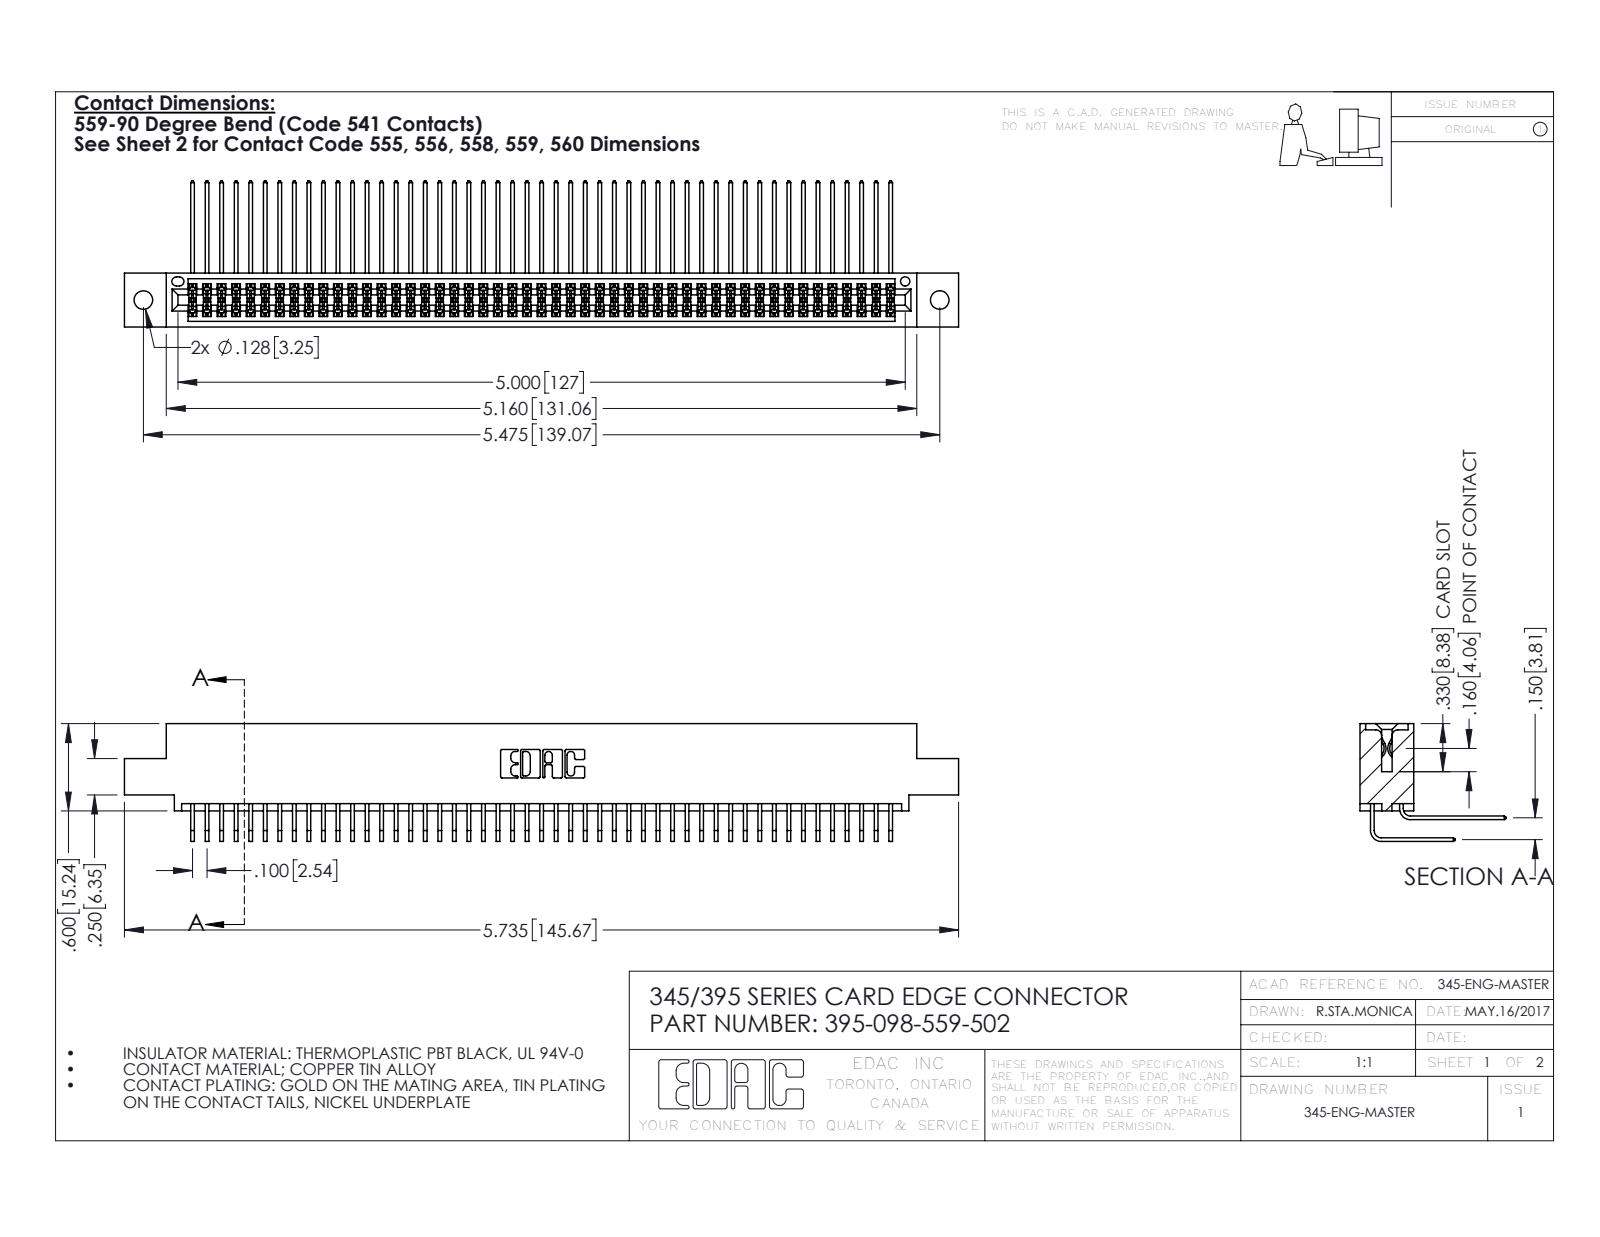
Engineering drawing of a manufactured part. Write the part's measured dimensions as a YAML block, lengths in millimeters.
part_name: "345-292-001_559 Tail - 2; 395-098-559-502; 345 Part_0.110 Offset - 0.128 Dia; 345-292-001_558 559 Tail - 1"
step_written_by: "SolidWorks 2016 (CONFIG_CONTROL_DESIGN)"
units: millimeters
bodies: {solids: 99, faces: 5226, planar: 3514, cylindrical: 1712, other: 0}
overall_size: [145.7, 25.5, 20.5]
volume: 14700
surface_area: 24300
round_holes:
  - {diameter: 3.3, count: 2}
  - {diameter: 1.6, count: 1}
partial_cylinders:
  - {radius: 0.2, count: 147}
  - {radius: 0.3, count: 22}
  - {radius: 0.2, count: 6}
  - {radius: 0.8, count: 6}
  - {radius: 0.7, count: 3}
  - {radius: 0.4, count: 2}
  - {radius: 0.5, count: 2}
  - {radius: 0.6, count: 2}
face_to_face_distances: [1.8, 7.6, 5.1, 9.4, 2.5, 6.9, 0.6, 5.7, 4.4, 3.8]
hole_center_spacings: [6.9, 133.1, 139.1]
